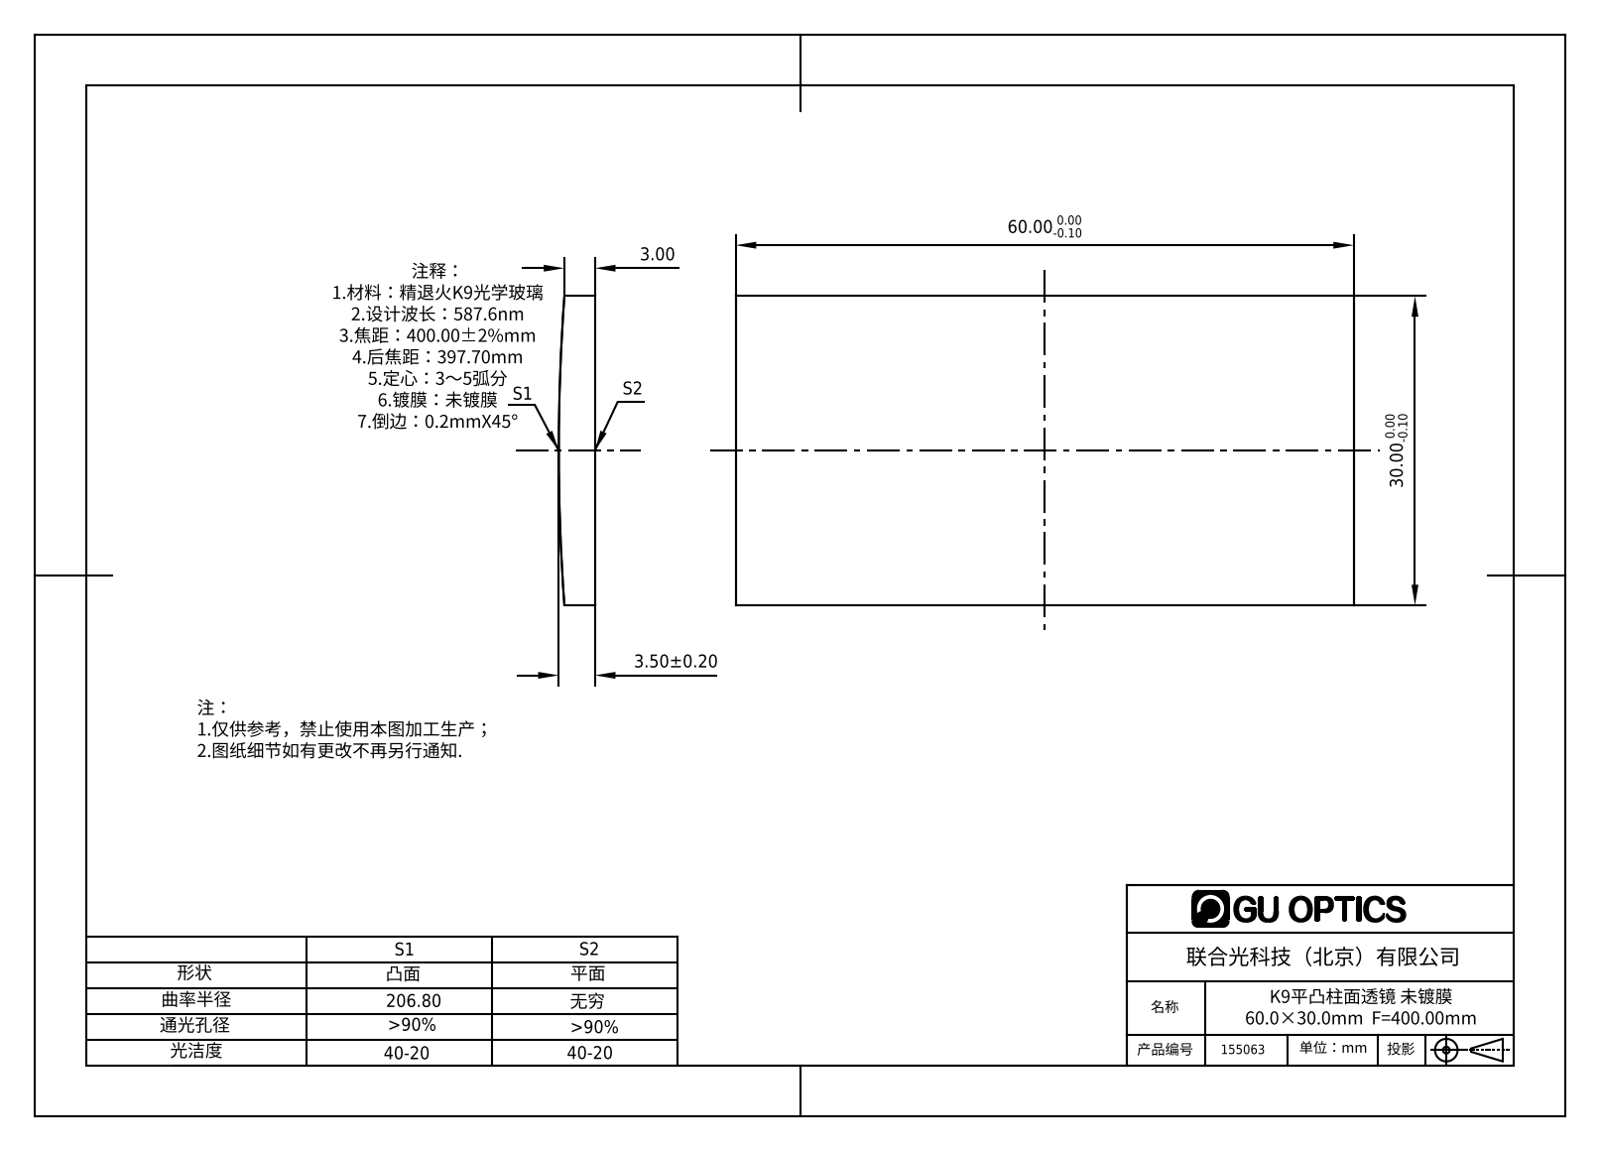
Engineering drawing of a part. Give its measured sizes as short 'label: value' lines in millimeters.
name: 155063
written by: SolidWorks 2016 (AUTOMOTIVE_DESIGN)
unit: mm
bodies: 1 solid, 6 faces (5 planar, 1 cylindrical, 0 other)
size: 60 × 30 × 3.5
volume: 5 973 mm³; area: 4 155 mm²
rounds: 1× R206.8
face distances: 30, 60
